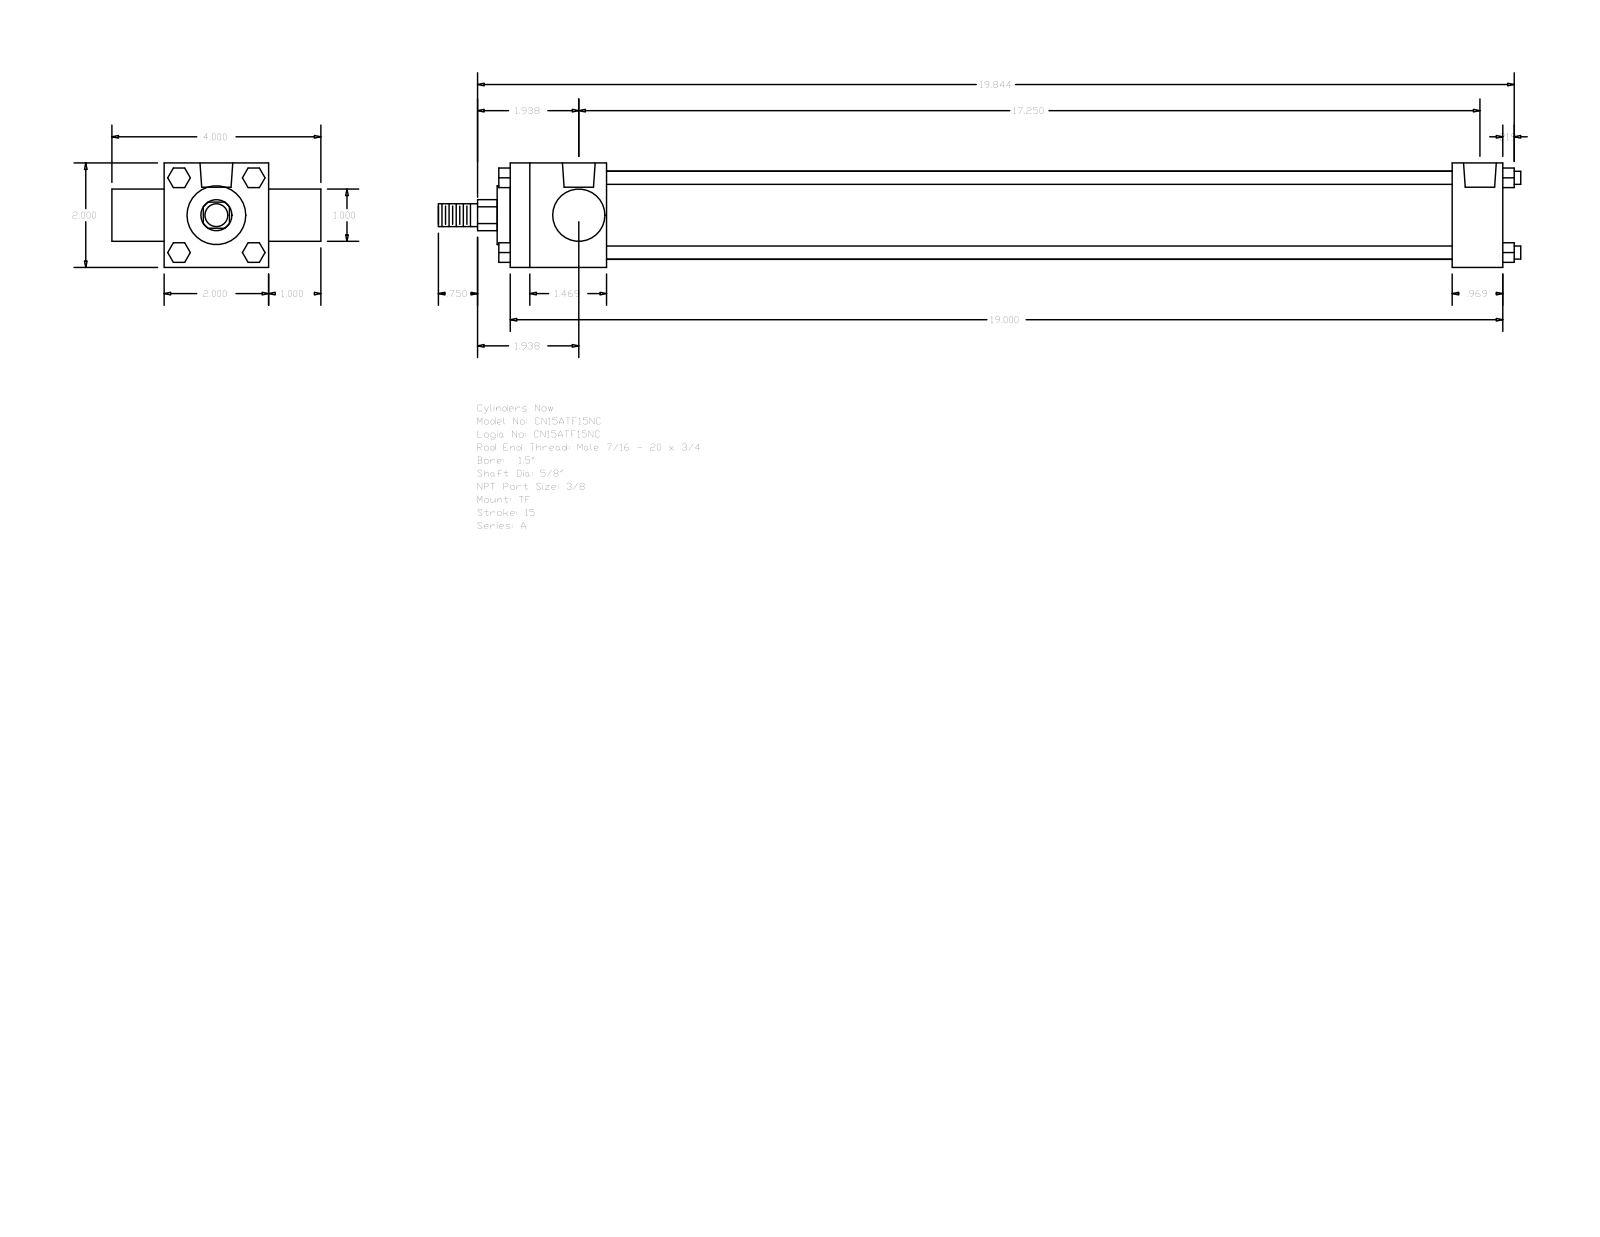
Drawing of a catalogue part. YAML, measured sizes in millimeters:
part_name: "A_TF__0150_0.625"
step_written_by: "GSSL Pune (CONFIG_CONTROL_DESIGN)"
units: millimeters
bodies: {solids: 0, faces: 120, planar: 92, cylindrical: 28, other: 0}
overall_size: [526.26, 101.6, 50.8]
round_holes:
  - {diameter: 5.56, count: 3}
  - {diameter: 15.93, count: 2}
round_bosses_or_shafts:
  - {diameter: 6.35, count: 4}
  - {diameter: 42.93, count: 1}
  - {diameter: 28.57, count: 1}
  - {diameter: 25.4, count: 1}
  - {diameter: 15.88, count: 1}
  - {diameter: 11.11, count: 1}
partial_cylinders:
  - {radius: 7.54, count: 1}
face_to_face_distances: [50.8, 482.6, 25.4, 76.2, 46.83, 457.99, 411.16, 435.77, 24.61, 101.6]
hole_center_spacings: [3.97, 434.18, 430.21, 438.15]
